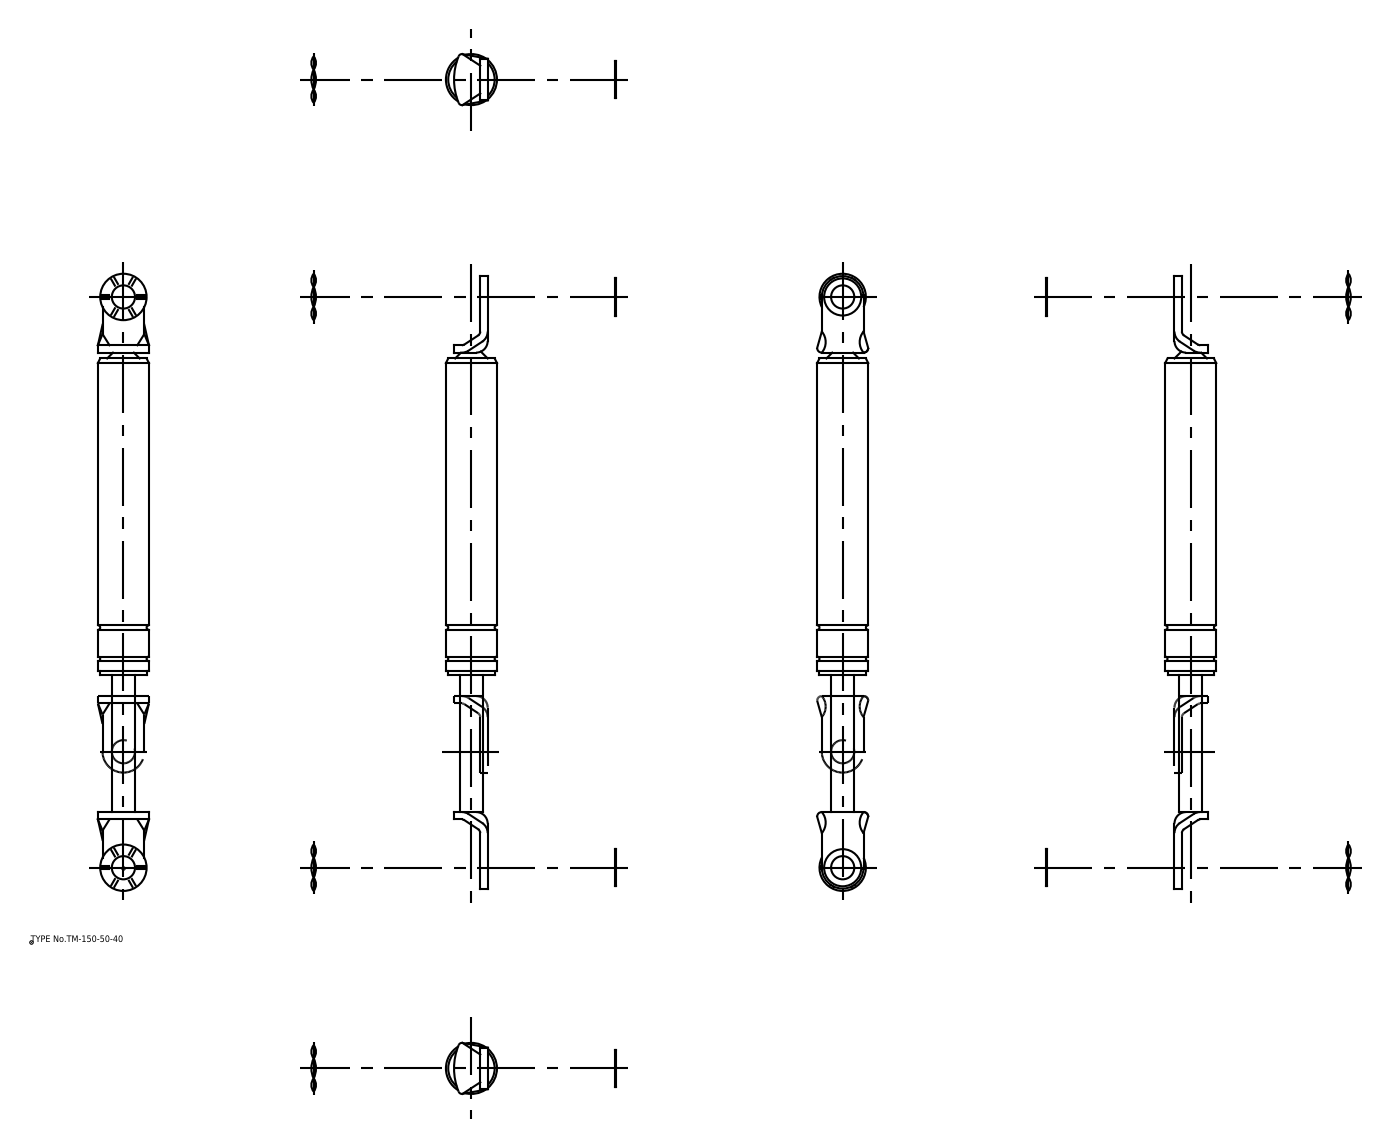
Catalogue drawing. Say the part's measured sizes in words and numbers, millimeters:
The part is named "ウェーブワッシャー; ワッシャー; 本体; 本体_div". Its 3-D file was written by "spGate 16.7.1 (AUTOMOTIVE_DESIGN)". It is 6 solids with 94 faces: 42 planar, 44 cylindrical and 8 other. Overall it measures 266 by 22.5 by 22.5 millimeters. Its volume is 62 228 cubic millimeters and its surface area 17 743 square millimeters. Round holes: 2 of diameter 10. Round bosses or shafts: 3 of diameter 20, 2 of diameter 16, 1 of diameter 22.5, 1 of diameter 22, 1 of diameter 10. Partial cylindrical surfaces (rounded edges, fillets, slot ends): 2 of radius 4.4, 2 of radius 5, 2 of radius 9, 1 of radius 26.32. The main face-to-face distances are 3.2, 2, 5.2, 201.2, 5.7, 3.7, 0.5, 142.2, 62.2, 204.4. The hole center spacings are 246.
